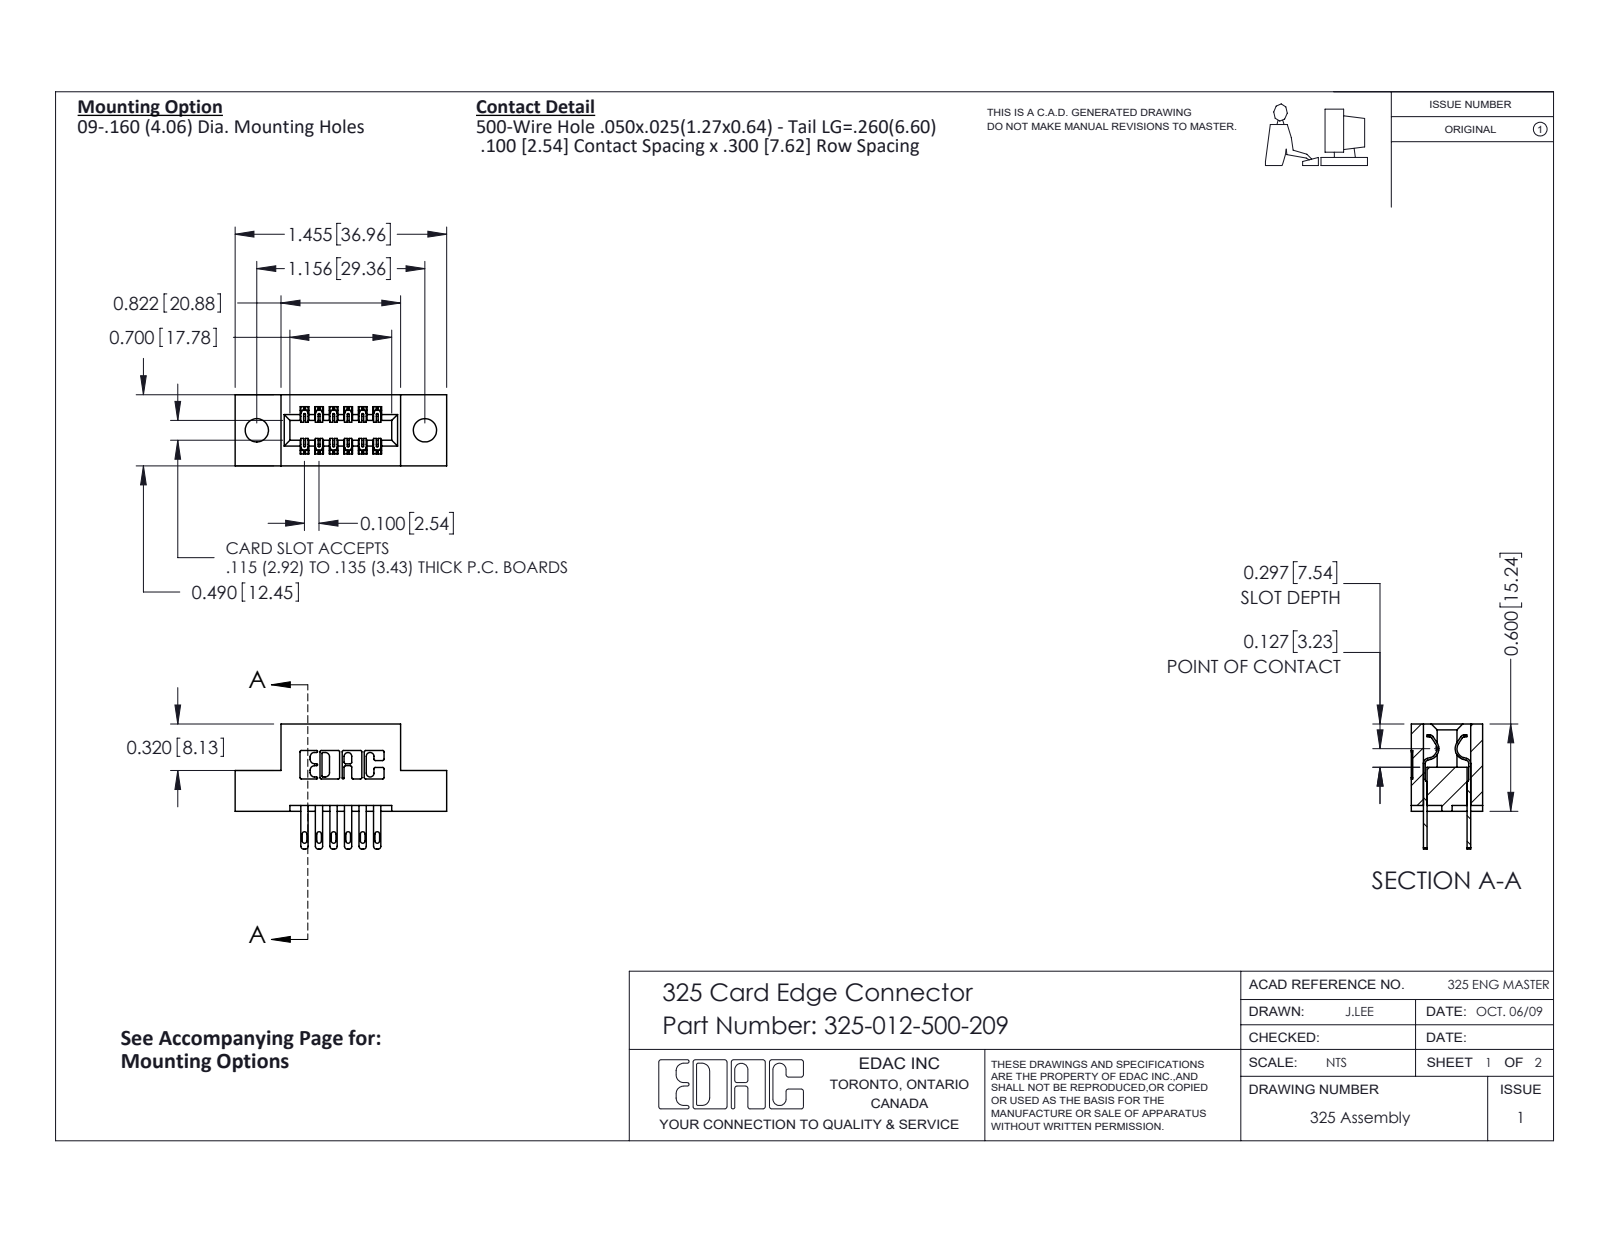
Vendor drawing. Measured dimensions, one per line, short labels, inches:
name: 325-012-500-209; 325 Part_.160 TH; 325-292-001_325-293-100
written by: SolidWorks 2016 (CONFIG_CONTROL_DESIGN)
unit: in
bodies: 13 solids, 690 faces (430 planar, 260 cylindrical, 0 other)
size: 1.455 × 0.86 × 0.49
volume: 0.26 in³; area: 6.728 in²
holes: 2× ⌀0.16
rounds: 22× R0.01, 18× R0.006, 12× R0.016, 12× R0.02, 6× R0.007, 6× R0.031, 3× R0.026, 2× R0.014
face distances: 0.3, 0.083, 0.407, 0.1, 0.04, 0.49, 0.2, 0.107, 0.383, 0.025
hole spacings: 1.156
